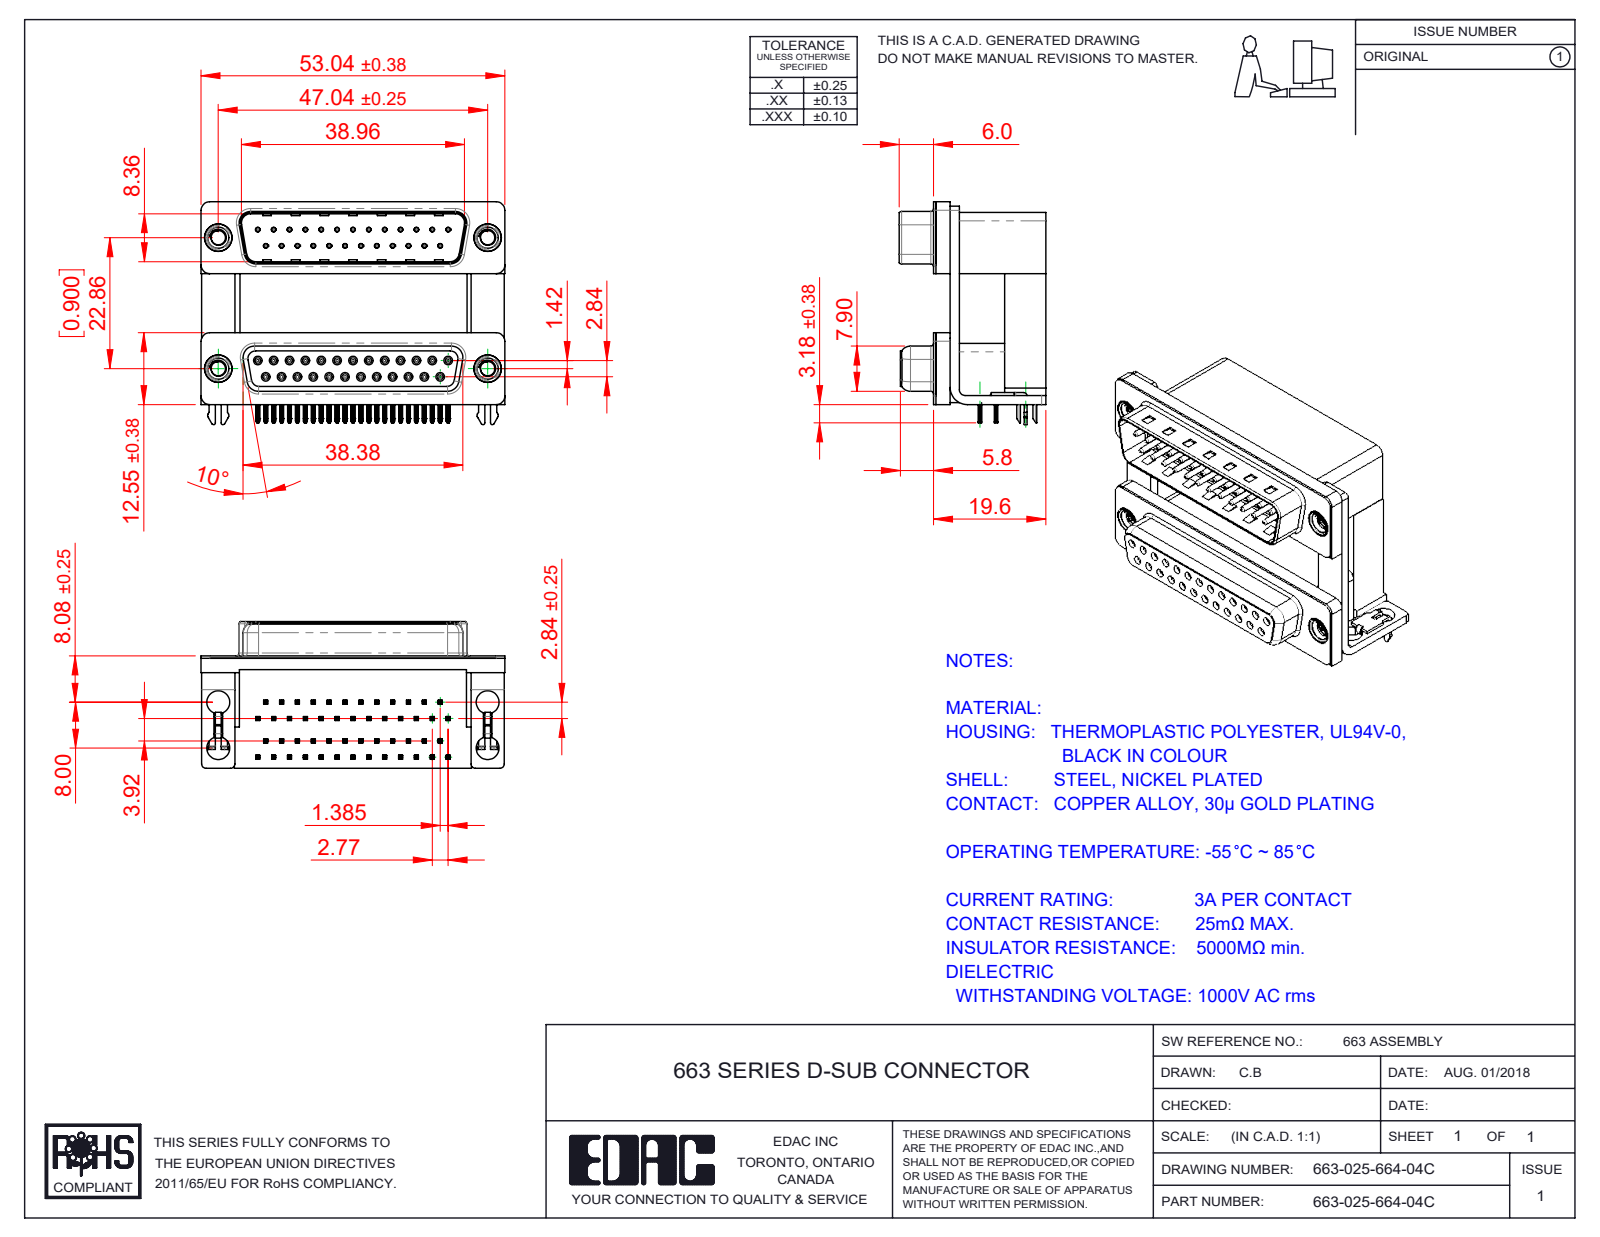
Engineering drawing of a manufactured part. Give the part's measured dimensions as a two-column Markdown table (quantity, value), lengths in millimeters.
| quantity | value |
| --- | --- |
| part name | 663 Contact Bottom Lower; 663-025-664-04C; 663 2 Prong Board Lock_4; 663 Contact Bottom Upper_H (+8 more) |
| STEP written by | SolidWorks 2020 (CONFIG_CONTROL_DESIGN) |
| units | millimeters |
| bodies | 63 solids, 6315 faces (3335 planar, 1581 cylindrical, 1399 other) |
| overall size | 53.04 × 38.91 × 25.6 |
| volume | 23 695 mm³ |
| surface area | 25 097 mm² |
| round holes (diameter × count) | 0.8 × 50, 0.35 × 25, 0.9 × 25, 4 × 8, 2.5 × 4, 3.5 × 4, 4.8 × 4, 5 × 4 |
| round bosses / shafts (diameter × count) | 1.2 × 25, 0.75 × 25, 4.9 × 4, 4.75 × 4, 3.9 × 4 |
| partial cylindrical surfaces (radius × count) | 0.1 × 201, 0.25 × 106, 0.15 × 100, 0.12 × 50, 0.35 × 50, 0.34 × 25, 0.5 × 16, 1.5 × 14 |
| main face-to-face distances | 19.2, 12, 7.2, 0.4, 10.7, 16.7, 9.5, 2.5, 22.86, 12.4 |
| hole center spacings | 3.16, 2.77, 5.54, 11.08, 8.31, 5.03, 13.85, 7.48 |
